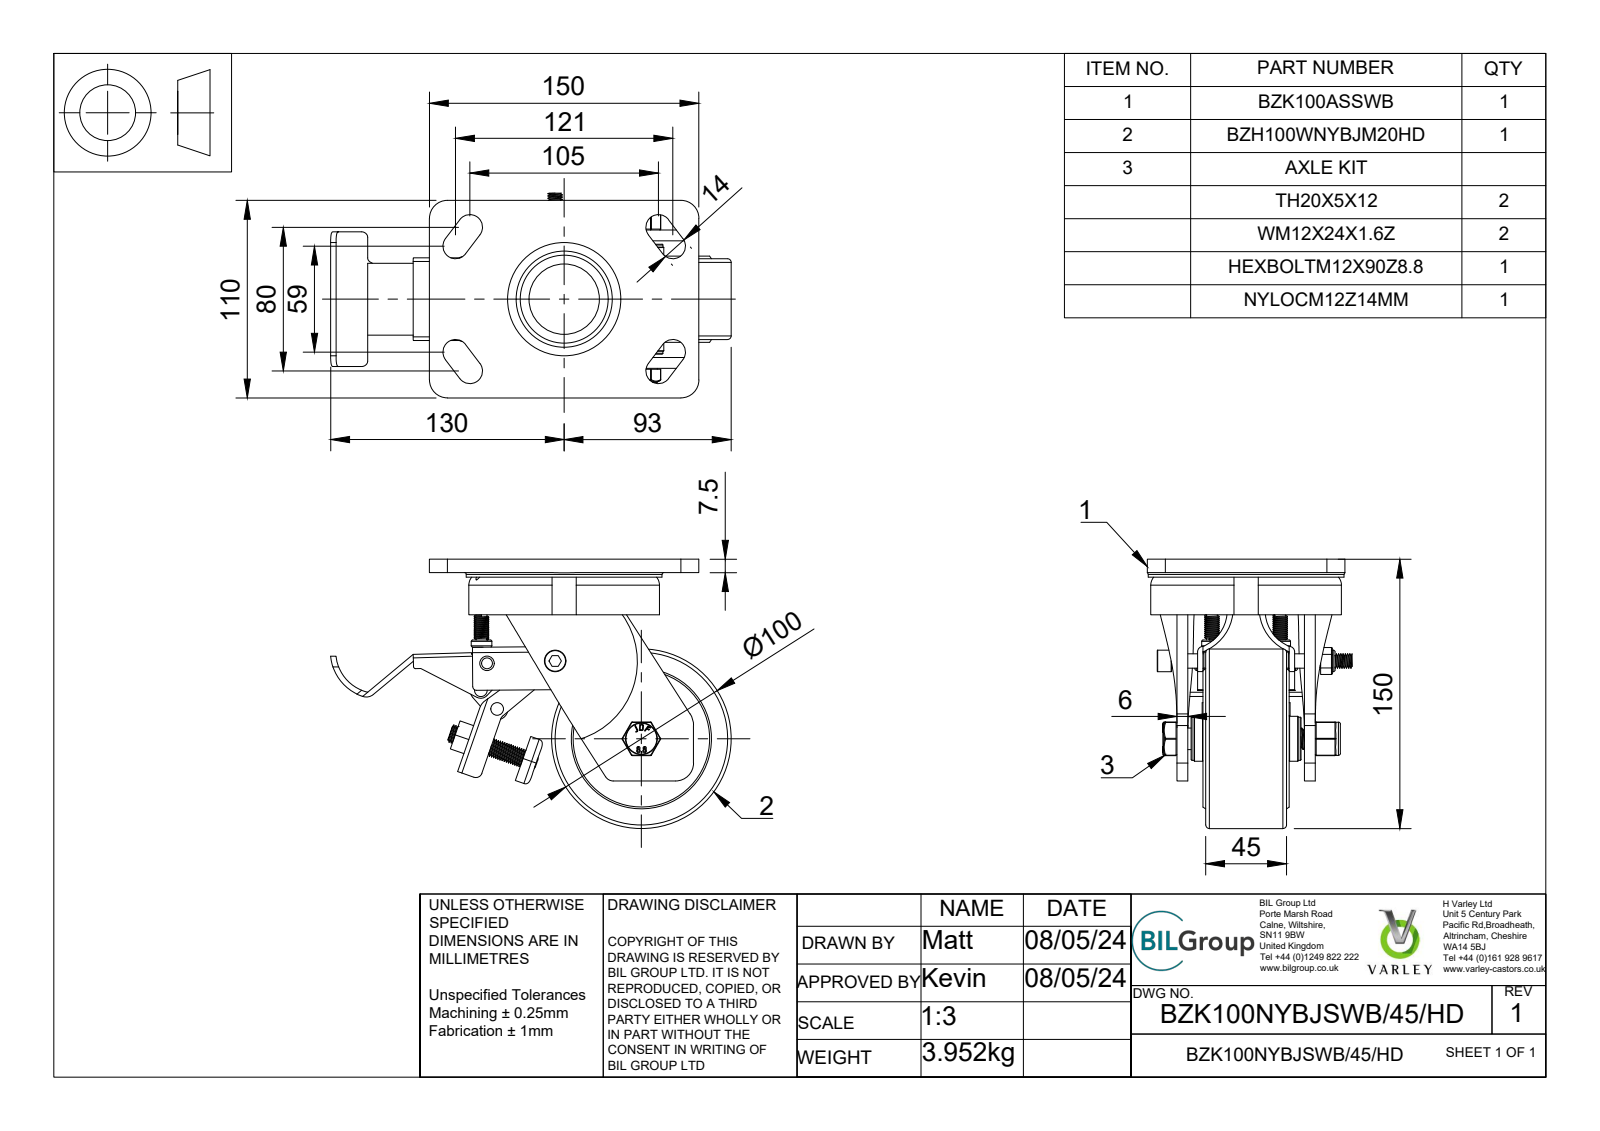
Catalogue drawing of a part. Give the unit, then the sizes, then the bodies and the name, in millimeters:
Units: millimetres
Overall size (bounding box): 223 × 150 × 114.01
Round holes (diameter × count): ⌀6 ×3, ⌀6.2 ×2, ⌀10 ×2, ⌀8 ×1, ⌀12 ×1, ⌀12.5 ×1, ⌀13 ×1, ⌀13.5 ×1, ⌀14 ×1, ⌀20 ×1, ⌀28.5 ×1, ⌀29.5 ×1
Round bosses / shafts (diameter × count): ⌀6 ×3, ⌀11.5 ×2, ⌀8 ×2, ⌀7 ×2, ⌀109 ×1, ⌀107 ×1, ⌀100 ×1, ⌀41.5 ×1
Partial cylindrical surfaces — rounded edges, fillets, slot ends (radius × count): R0.5 ×26, R7 ×9, R3 ×6, R6 ×5, R10 ×5, R0.47 ×4, R0.9 ×4, R1 ×3
Main face-to-face distances: 7.5, 31, 10, 3, 23.5, 46.5, 0.5, 1, 47, 12.5
Hole centre spacings: 49.77, 13.8, 15.35, 26.02, 38, 38.01, 41.97, 44.48
Volume: 760 441 mm³ · Surface area: 233 869 mm²
Bodies: 53 solids, 921 faces (396 planar, 349 cylindrical, 176 other)
Part name (STEP PRODUCT): BZK100NYBJSWB/45/HD v3; BZK100ASSWB v1; FABRICATED STEEL TOP PLATE; FABRICATED STEEL FORKS (+8 more)
STEP written by: Autodesk Translation Framework v12.20.1.177 (AUTOMOTIVE_DESIGN)
